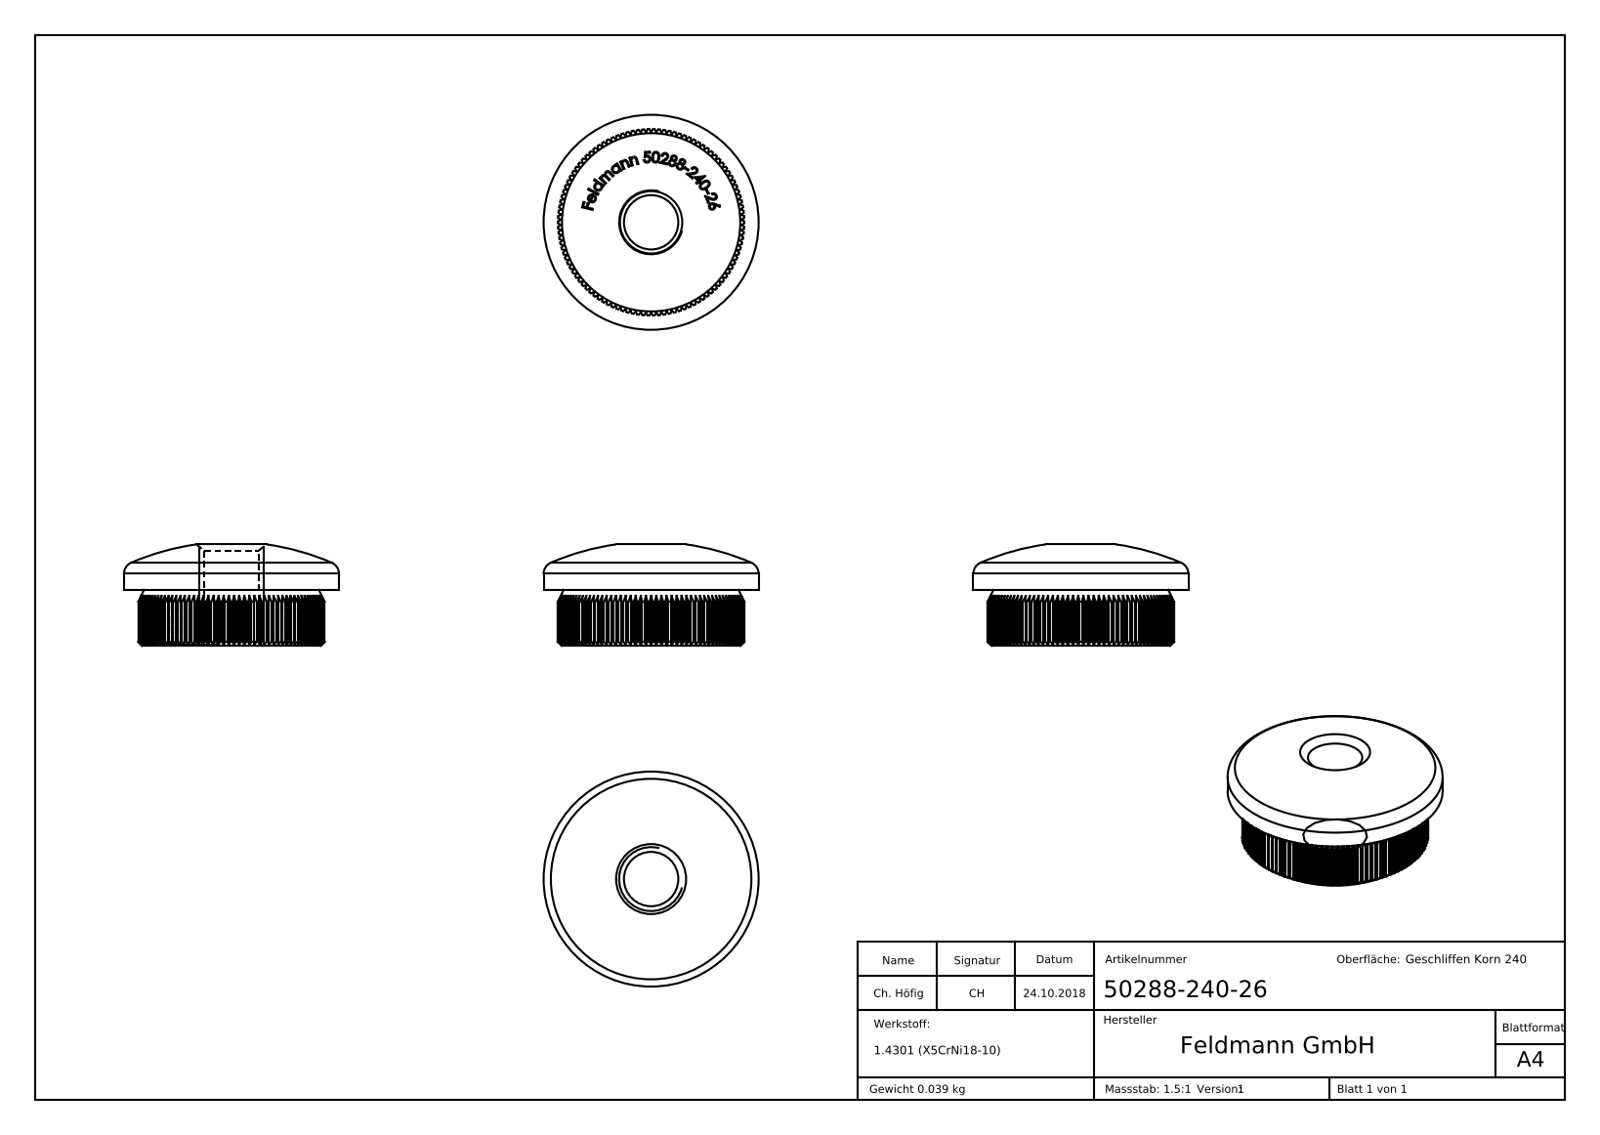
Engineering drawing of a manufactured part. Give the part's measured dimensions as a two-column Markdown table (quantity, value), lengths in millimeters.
| quantity | value |
| --- | --- |
| part name | 50288-240-26 |
| STEP written by | SolidWorks 2015 (CONFIG_CONTROL_DESIGN) |
| units | millimeters |
| bodies | 1 solid, 529 faces (332 planar, 114 cylindrical, 83 other) |
| overall size | 26.9 × 26.9 × 12.7 |
| volume | 4 972 mm³ |
| surface area | 2 375 mm² |
| round holes (diameter × count) | 6.8 × 1 |
| round bosses / shafts (diameter × count) | 26.9 × 1 |
| partial cylindrical surfaces (radius × count) | 11.65 × 1 |
| main face-to-face distances | 11.3, 7, 11.32, 11.28, 6.9, 0.66, 0.79, 0.72, 1.32, 1.45 |
